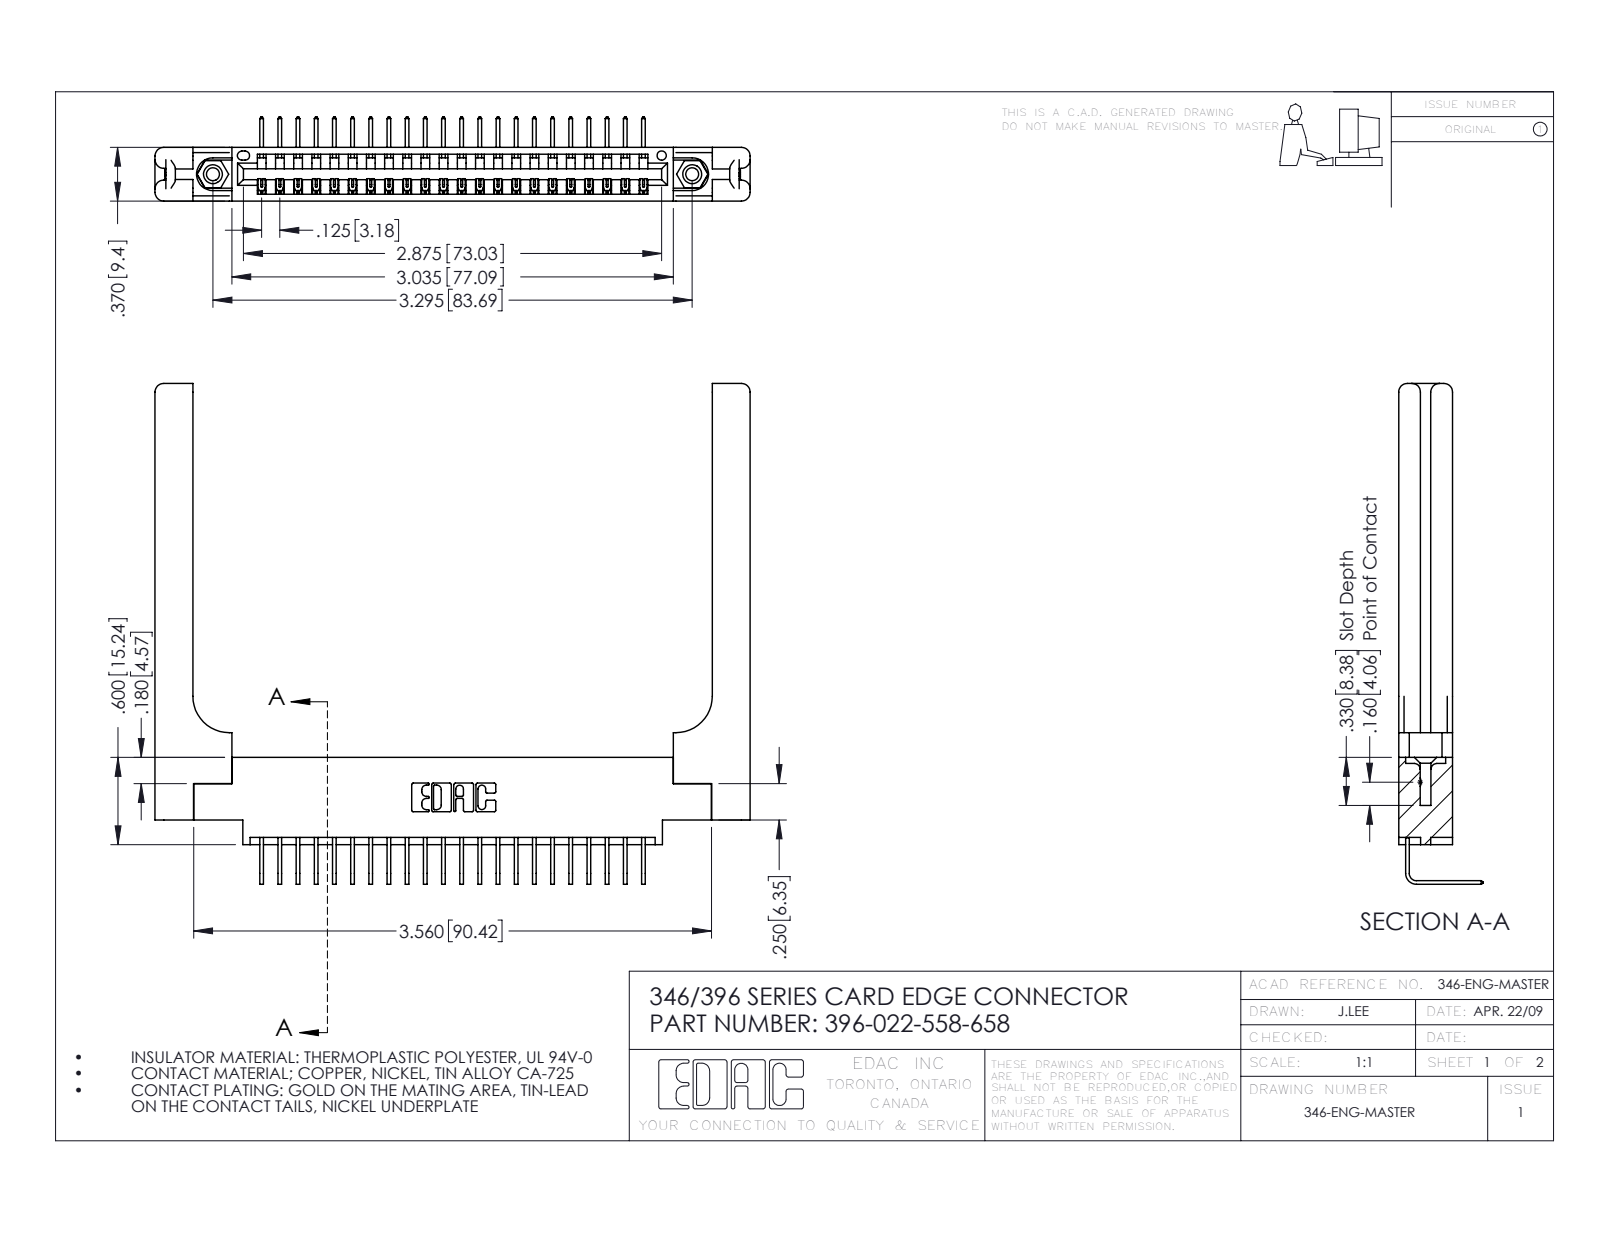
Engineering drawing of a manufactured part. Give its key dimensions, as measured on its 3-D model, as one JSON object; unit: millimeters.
{"part_name": "346-220-058_345-220-058; 345-292-001_558 Tail - 2; 396-022-558-658; 346 Part_0.170 Offset - 0.156 Dia-TH (+1 more)", "step_written_by": "SolidWorks 2016 (CONFIG_CONTROL_DESIGN)", "units": "millimeters", "bodies": {"solids": 27, "faces": 1702, "planar": 1152, "cylindrical": 490, "other": 60}, "overall_size": [103.9, 87.5, 14.7], "volume_mm3": 17240, "surface_area_mm2": 17710, "round_holes": [[2.3, 2], [3.2, 2], [4, 2], [1.6, 1]], "round_bosses_or_shafts": [[3.9, 2]], "partial_cylinders_radius": [[0.2, 44], [0.3, 22], [1.5, 16], [0.2, 6], [0.8, 6], [0.7, 3], [0.8, 2], [0.8, 2]], "face_to_face_distances": [9.4, 1.8, 8.2, 3.8, 1.2, 3.8, 6.4, 0.6, 7.6, 5.6], "hole_center_spacings": [6.2, 78.4, 83.7]}
